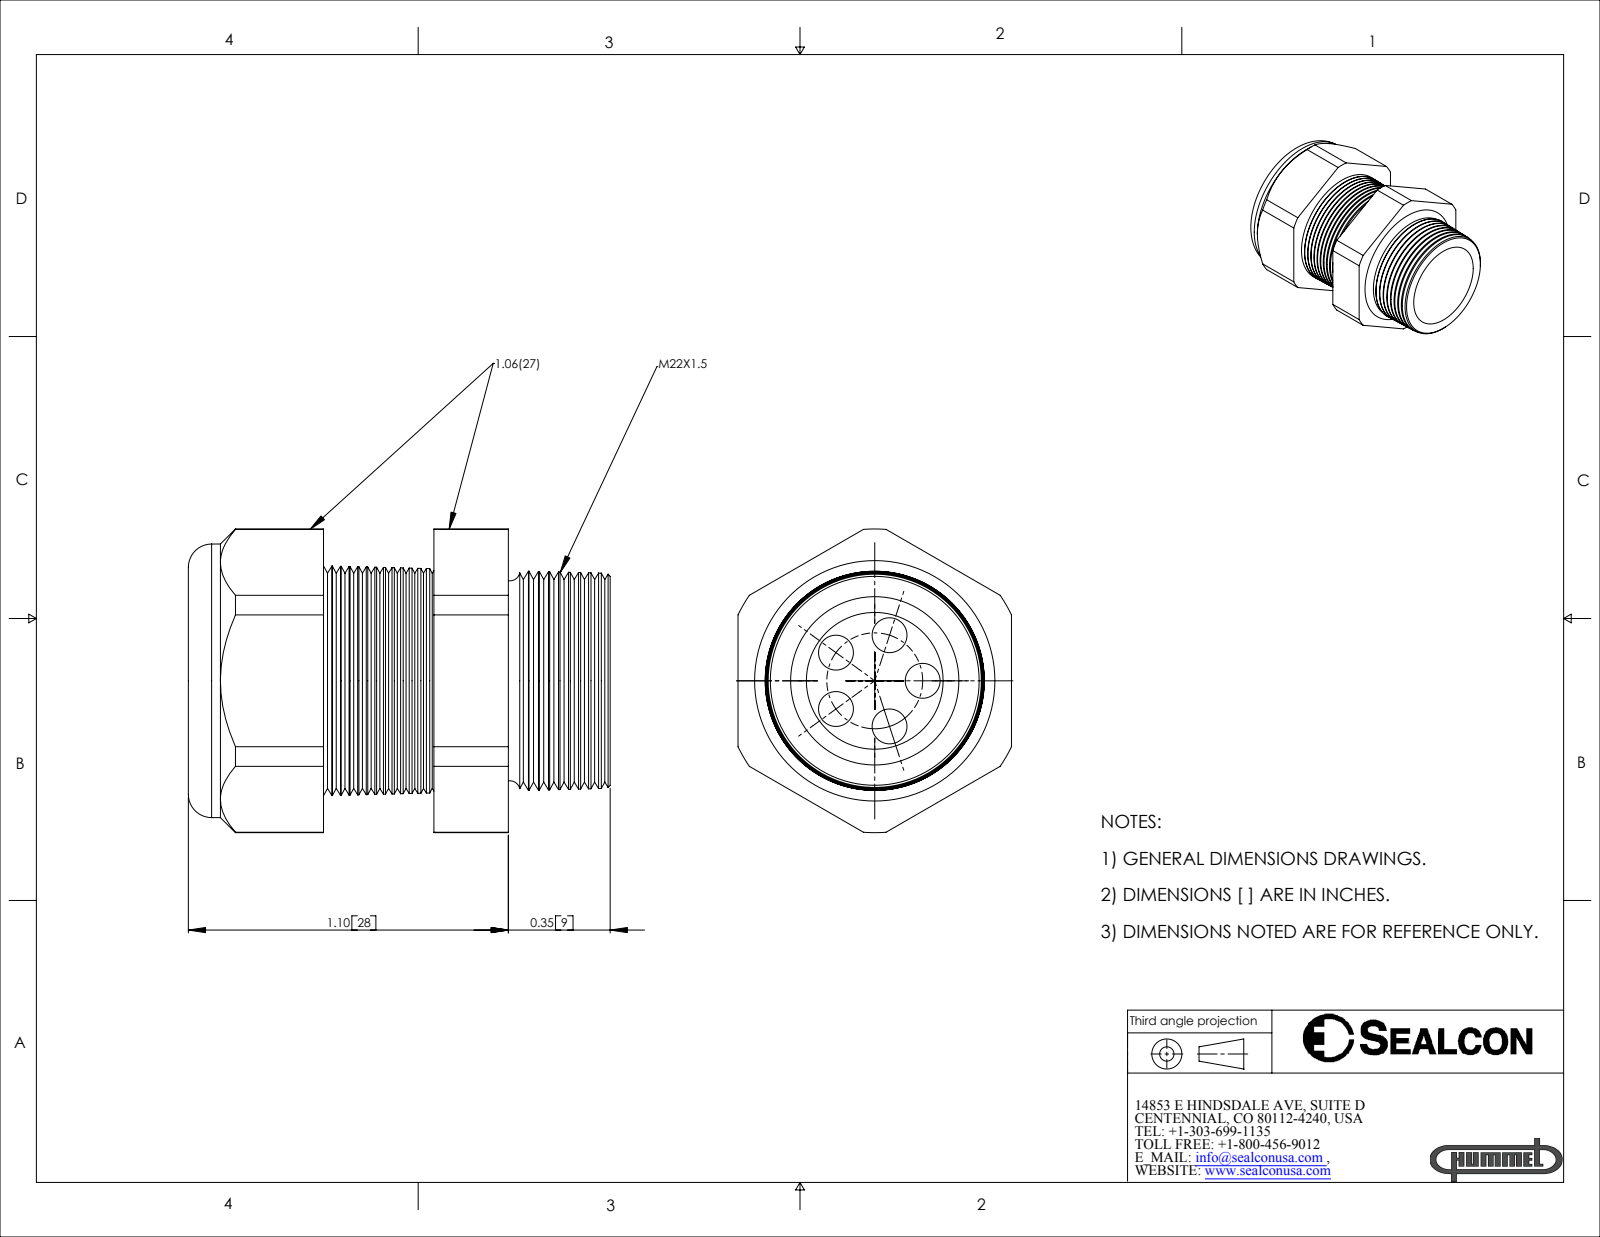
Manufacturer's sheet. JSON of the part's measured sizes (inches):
{"part_name": "CD22M4-BK", "step_written_by": "SolidWorks 2007 (CONFIG_CONTROL_DESIGN)", "units": "inches", "bodies": {"solids": 2, "faces": 196, "planar": 20, "cylindrical": 30, "other": 146}, "overall_size": [1.45, 1.043, 0.94], "volume_in3": 0.582, "surface_area_in2": 10.34, "round_holes": [[0.12, 5], [0.45, 1], [0.47, 1]], "round_bosses_or_shafts": [[0.94, 1]], "partial_cylinders_radius": [[0.522, 1]], "face_to_face_distances": [0.94, 0.844, 0.465, 0.38, 1.1, 0.635, 0.256, 1.45, 0.985, 0.606], "hole_center_spacings": [0.194, 0.313, 0.165, 0.165]}
